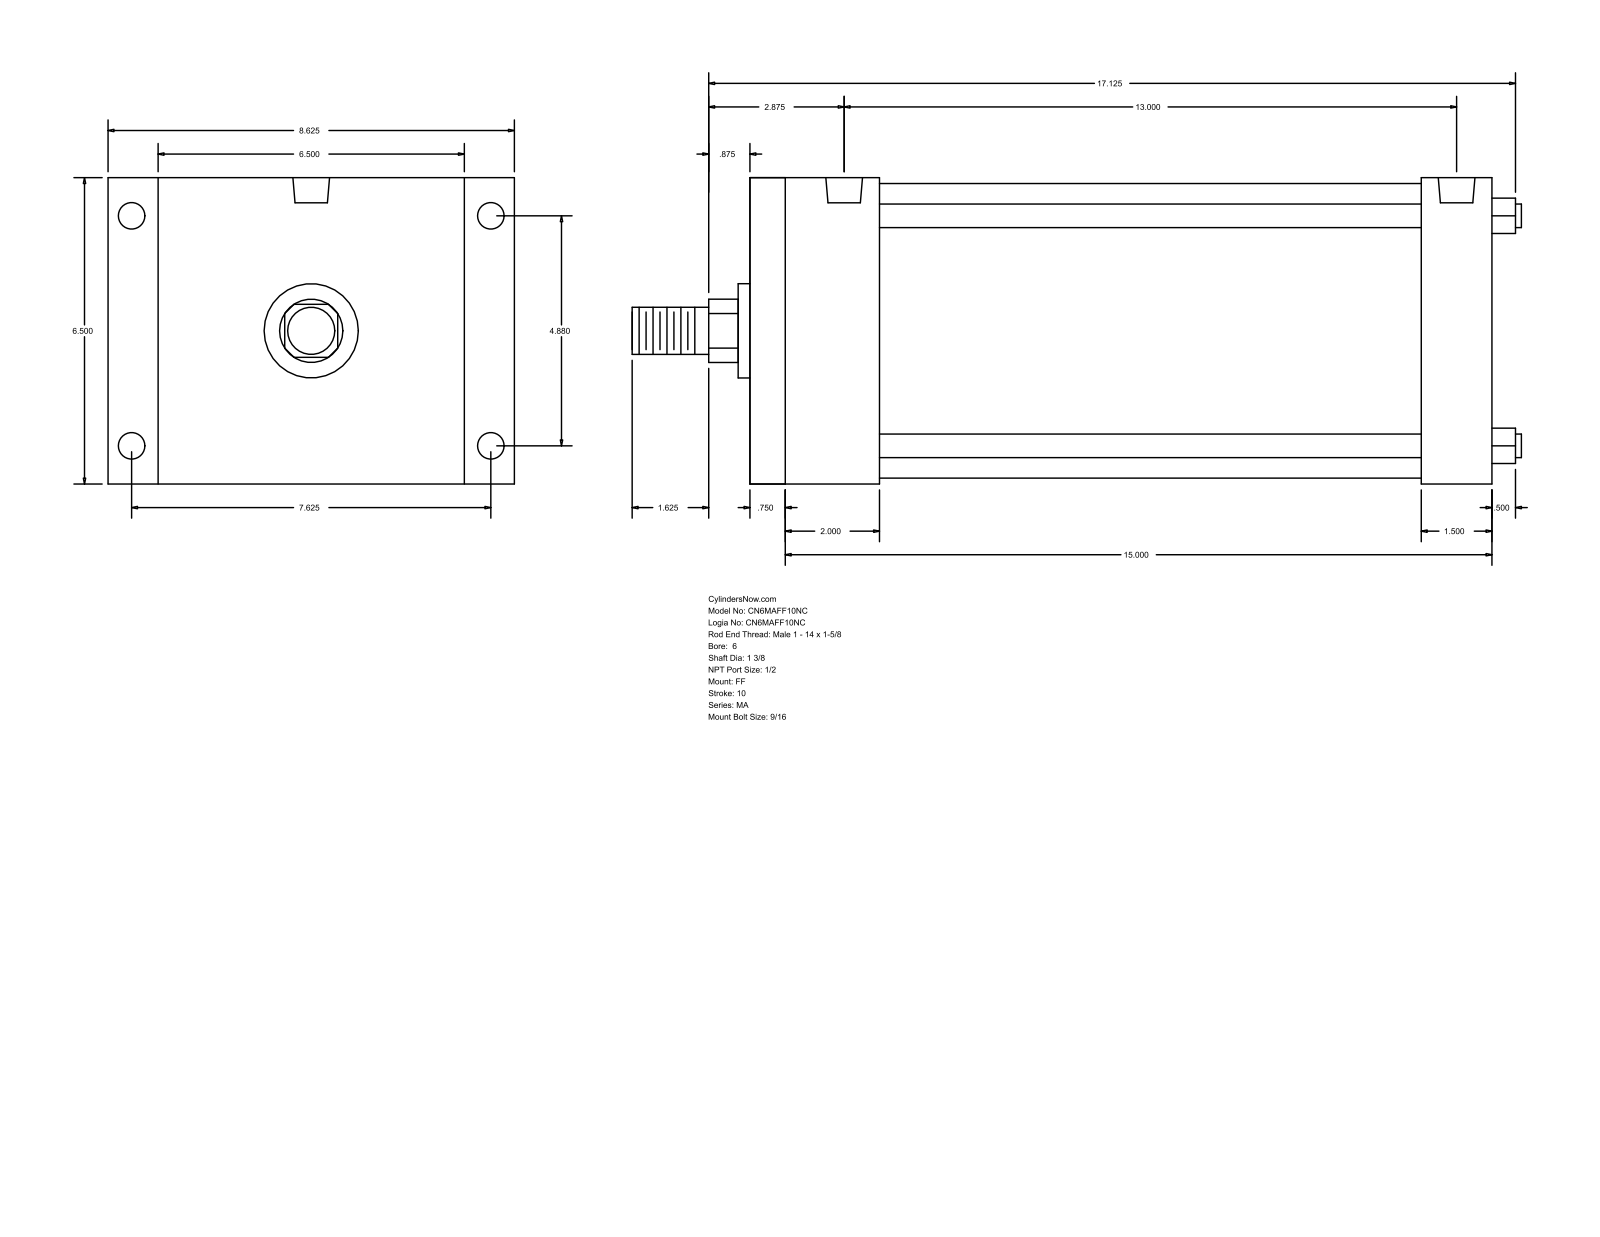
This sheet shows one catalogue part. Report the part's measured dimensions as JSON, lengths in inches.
{"part_name": "MA_FF__0600_1.375", "step_written_by": "GSSL Pune (CONFIG_CONTROL_DESIGN)", "units": "inches", "bodies": {"solids": 0, "faces": 92, "planar": 64, "cylindrical": 28, "other": 0}, "overall_size": [18.875, 8.625, 6.5], "round_holes": [[0.563, 4], [0.687, 4], [0.778, 2]], "round_bosses_or_shafts": [[0.5, 4], [6.25, 1], [2, 1], [1.375, 1], [1, 1]], "partial_cylinders_radius": [[0.672, 1]], "face_to_face_distances": [6.5, 15.75, 0.625, 15.125, 2, 13.625, 2.625, 13.125, 14.25, 11.625], "hole_center_spacings": [4.88, 7.625, 9.053, 13.125, 0.125, 13]}
